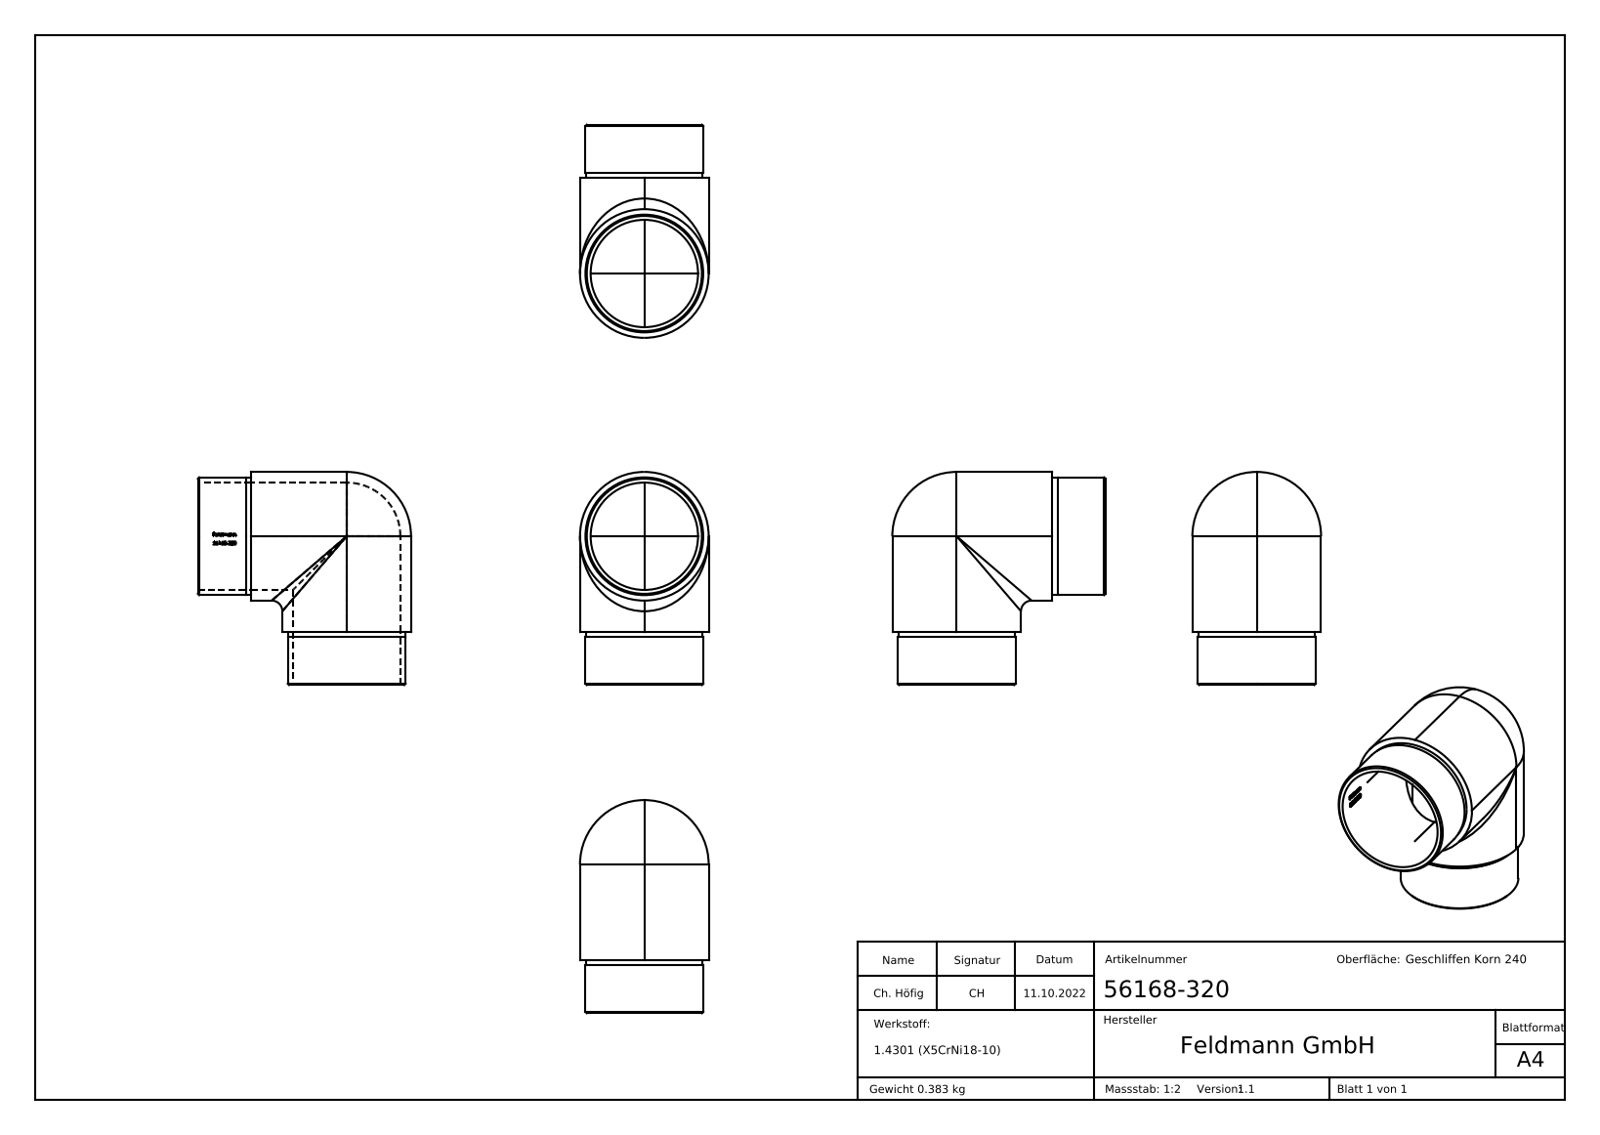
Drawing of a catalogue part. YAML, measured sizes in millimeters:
part_name: "56168-320"
step_written_by: "SolidWorks 2018 (CONFIG_CONTROL_DESIGN)"
units: millimeters
bodies: {solids: 1, faces: 258, planar: 91, cylindrical: 39, other: 128}
overall_size: [80, 80, 48.3]
volume: 48534
surface_area: 30865
round_holes:
  - {diameter: 40.3, count: 2}
round_bosses_or_shafts:
  - {diameter: 48.3, count: 2}
  - {diameter: 44.2, count: 2}
  - {diameter: 43.8, count: 2}
partial_cylinders:
  - {radius: 20.65, count: 1}
face_to_face_distances: [20, 18, 2, 0.39, 1.26, 2.97, 4.23, 1.32, 3.66, 3.27]
